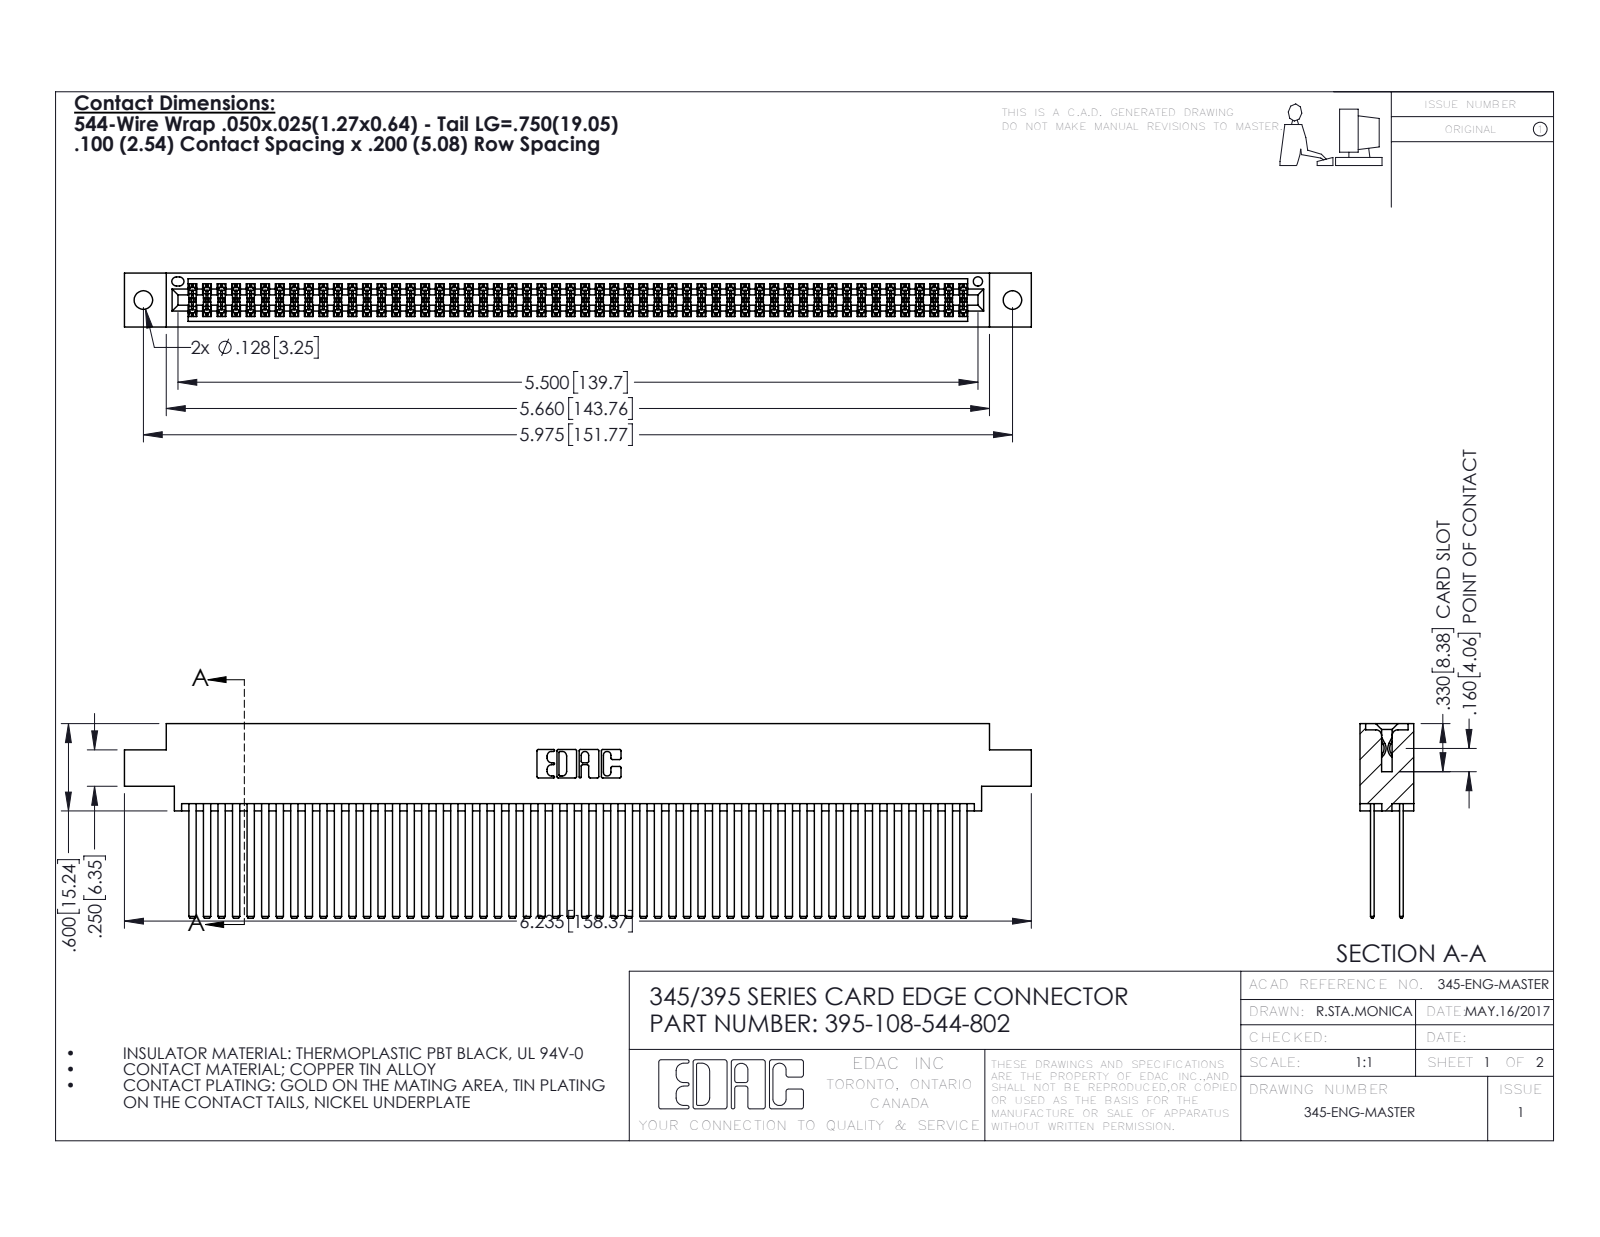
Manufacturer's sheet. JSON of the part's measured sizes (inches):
{"part_name": "345 Part_0.170 Offset - 0.128 Dia; 345-292-001_345-293-144; 395-108-544-802", "step_written_by": "SolidWorks 2016 (CONFIG_CONTROL_DESIGN)", "units": "inches", "bodies": {"solids": 109, "faces": 4882, "planar": 3216, "cylindrical": 1666, "other": 0}, "overall_size": [6.235, 1.337, 0.37], "volume_in3": 1.029, "surface_area_in2": 45.67, "round_holes": [[0.128, 2], [0.064, 1]], "partial_cylinders_radius": [[0.006, 162], [0.01, 22], [0.007, 6], [0.031, 6], [0.026, 3], [0.014, 2], [0.019, 2], [0.022, 2]], "face_to_face_distances": [0.2, 0.025, 0.072, 0.098, 0.272, 0.298, 0.225, 0.175, 0.37, 0.15], "hole_center_spacings": [0.27, 5.739, 5.975]}
